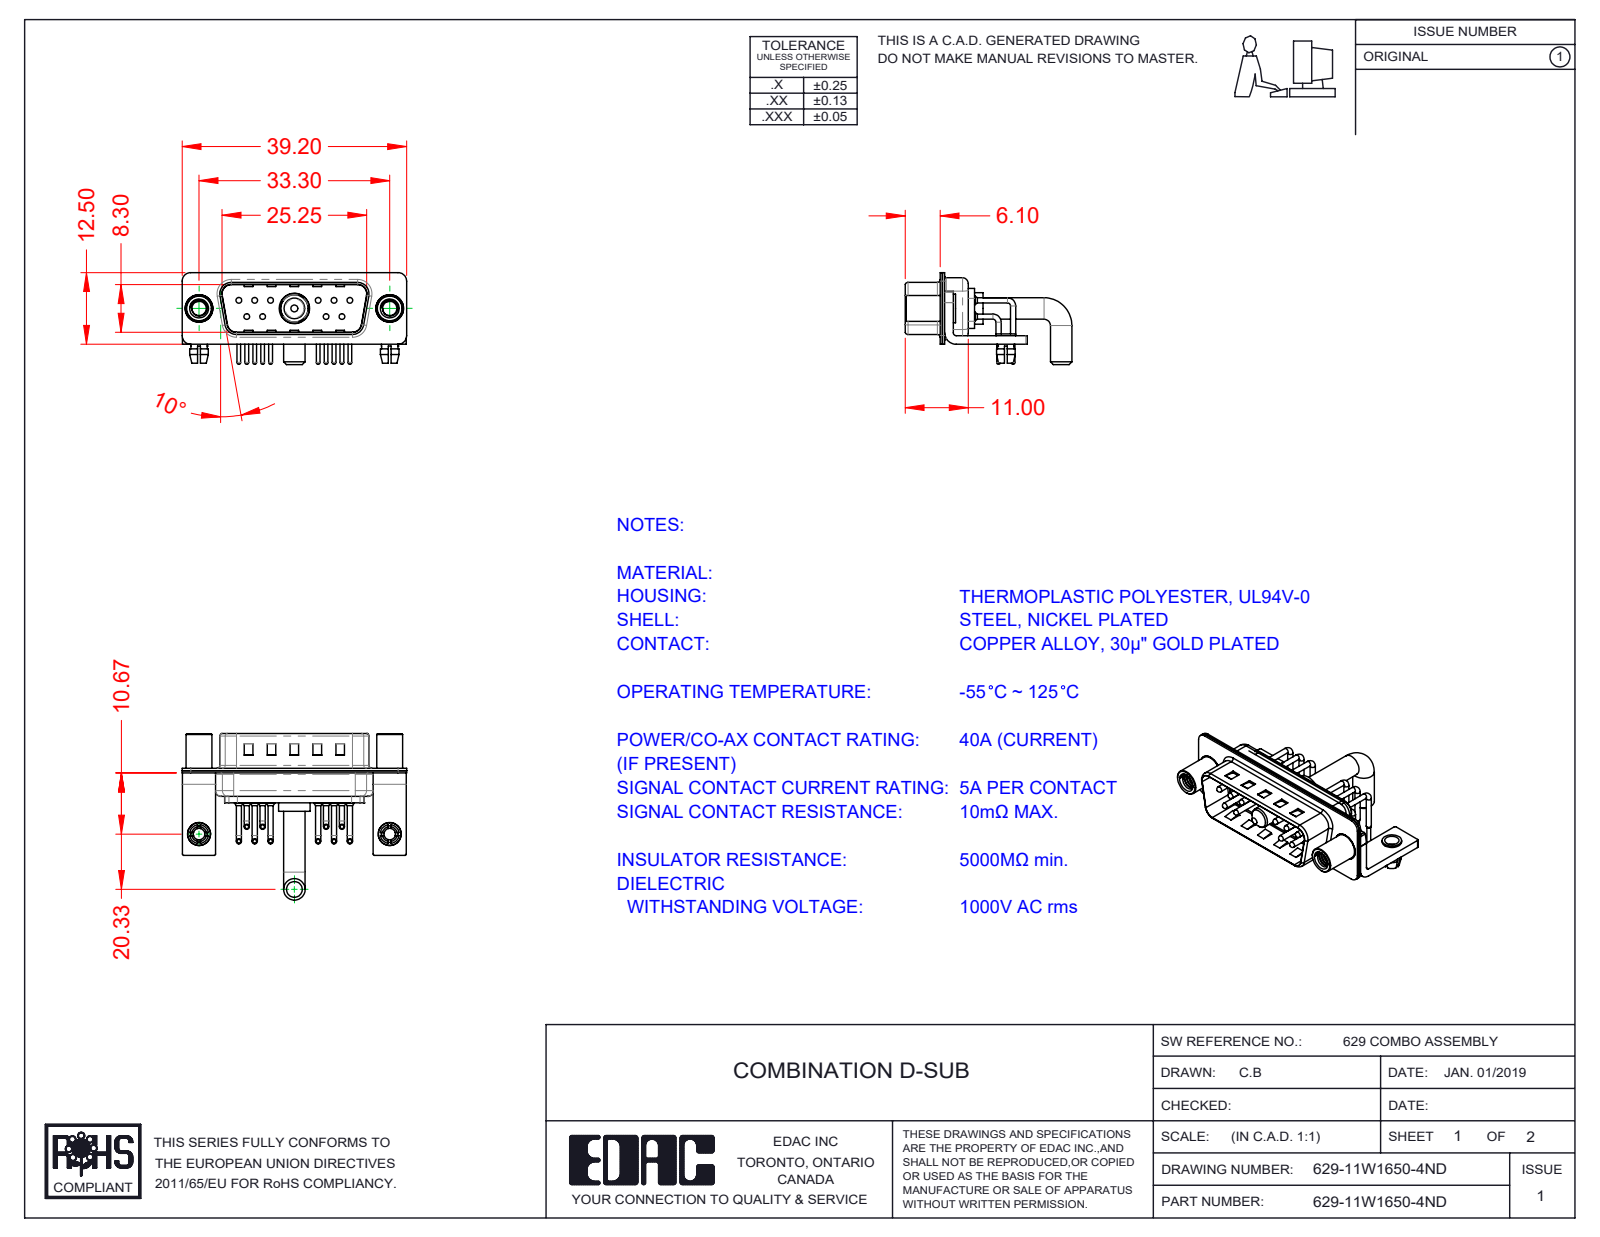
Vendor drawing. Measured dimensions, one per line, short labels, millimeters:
name: 629-11W1650-4ND; 629Combo Contact Row 2; 629Combo Threaded Standoff_D; 629Combo Housing_11W1 (+6 more)
written by: SolidWorks 2020 (CONFIG_CONTROL_DESIGN)
unit: mm
bodies: 21 solids, 1686 faces (868 planar, 622 cylindrical, 196 other)
size: 39.2 × 29.11 × 16.05
volume: 2 635 mm³; area: 6 496 mm²
holes: 12× ⌀2, 10× ⌀0.75, 10× ⌀1.6, 4× ⌀2.5, 2× ⌀3.2, 2× ⌀4, 2× ⌀4.8, 1× ⌀4.85, 1× ⌀5.3
bosses: 20× ⌀0.9, 10× ⌀1.5, 10× ⌀1, 10× ⌀0.65, 2× ⌀5, 2× ⌀4.9, 2× ⌀4.5, 2× ⌀4
rounds: 16× R0.25, 16× R1.5, 13× R2, 10× R1.01, 9× R0.5, 8× R1.6, 7× R1, 4× R0.6
face distances: 0.4, 0.8, 1.5, 9.5, 9.1, 8.7, 9.9, 0.6, 1.9, 2.1
hole spacings: 3.16, 2.77, 13.85, 11.08, 16.62, 5.03, 5.04, 5.54
